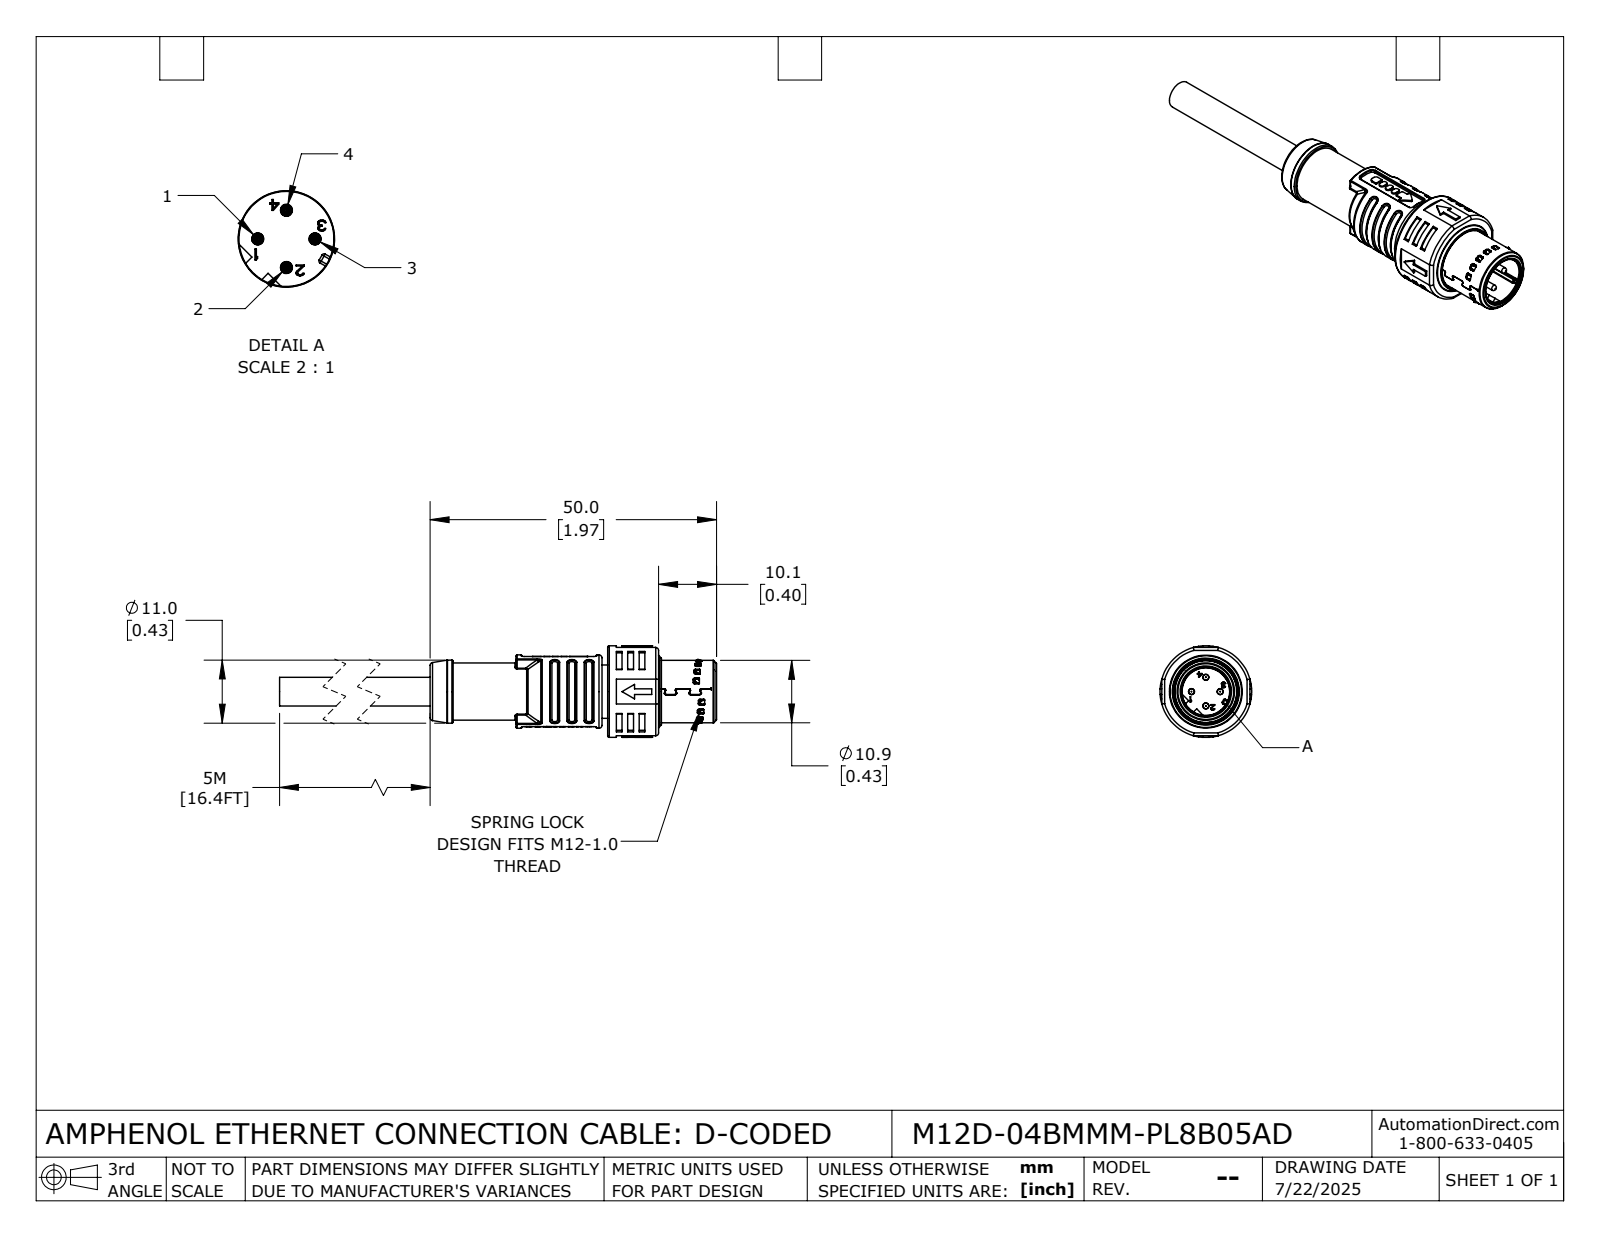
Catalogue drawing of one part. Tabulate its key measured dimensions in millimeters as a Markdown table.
| quantity | value |
| --- | --- |
| part name | M12D-04BMMM-PL8B05AD |
| STEP written by | SolidWorks 2024 (CONFIG_CONTROL_DESIGN) |
| units | millimeters |
| bodies | 1 solid, 2139 faces (996 planar, 644 cylindrical, 499 other) |
| overall size | 80 × 16 × 16 |
| volume | 5 399 mm³ |
| surface area | 5 961 mm² |
| round holes (diameter × count) | 1.05 × 4, 8.3 × 1, 9 × 1, 10.15 × 1, 10.5 × 1, 10.9 × 1, 11.5 × 1, 11.8 × 1, 14.2 × 1 |
| round bosses / shafts (diameter × count) | 1 × 4, 16 × 1, 14.1 × 1, 12.8 × 1, 12.4 × 1, 11 × 1, 10.45 × 1, 10.4 × 1 |
| partial cylindrical surfaces (radius × count) | 0.2 × 119, 0.25 × 66, 0.3 × 64, 0.15 × 44, 0.5 × 38, 0.13 × 12, 0.7 × 11, 0.1 × 7 |
| main face-to-face distances | 1, 30, 10.1, 8.9, 2.5, 1.2, 8.6, 32.5, 15.4, 1.5 |
| hole center spacings | 2.5, 3.54, 5 |
